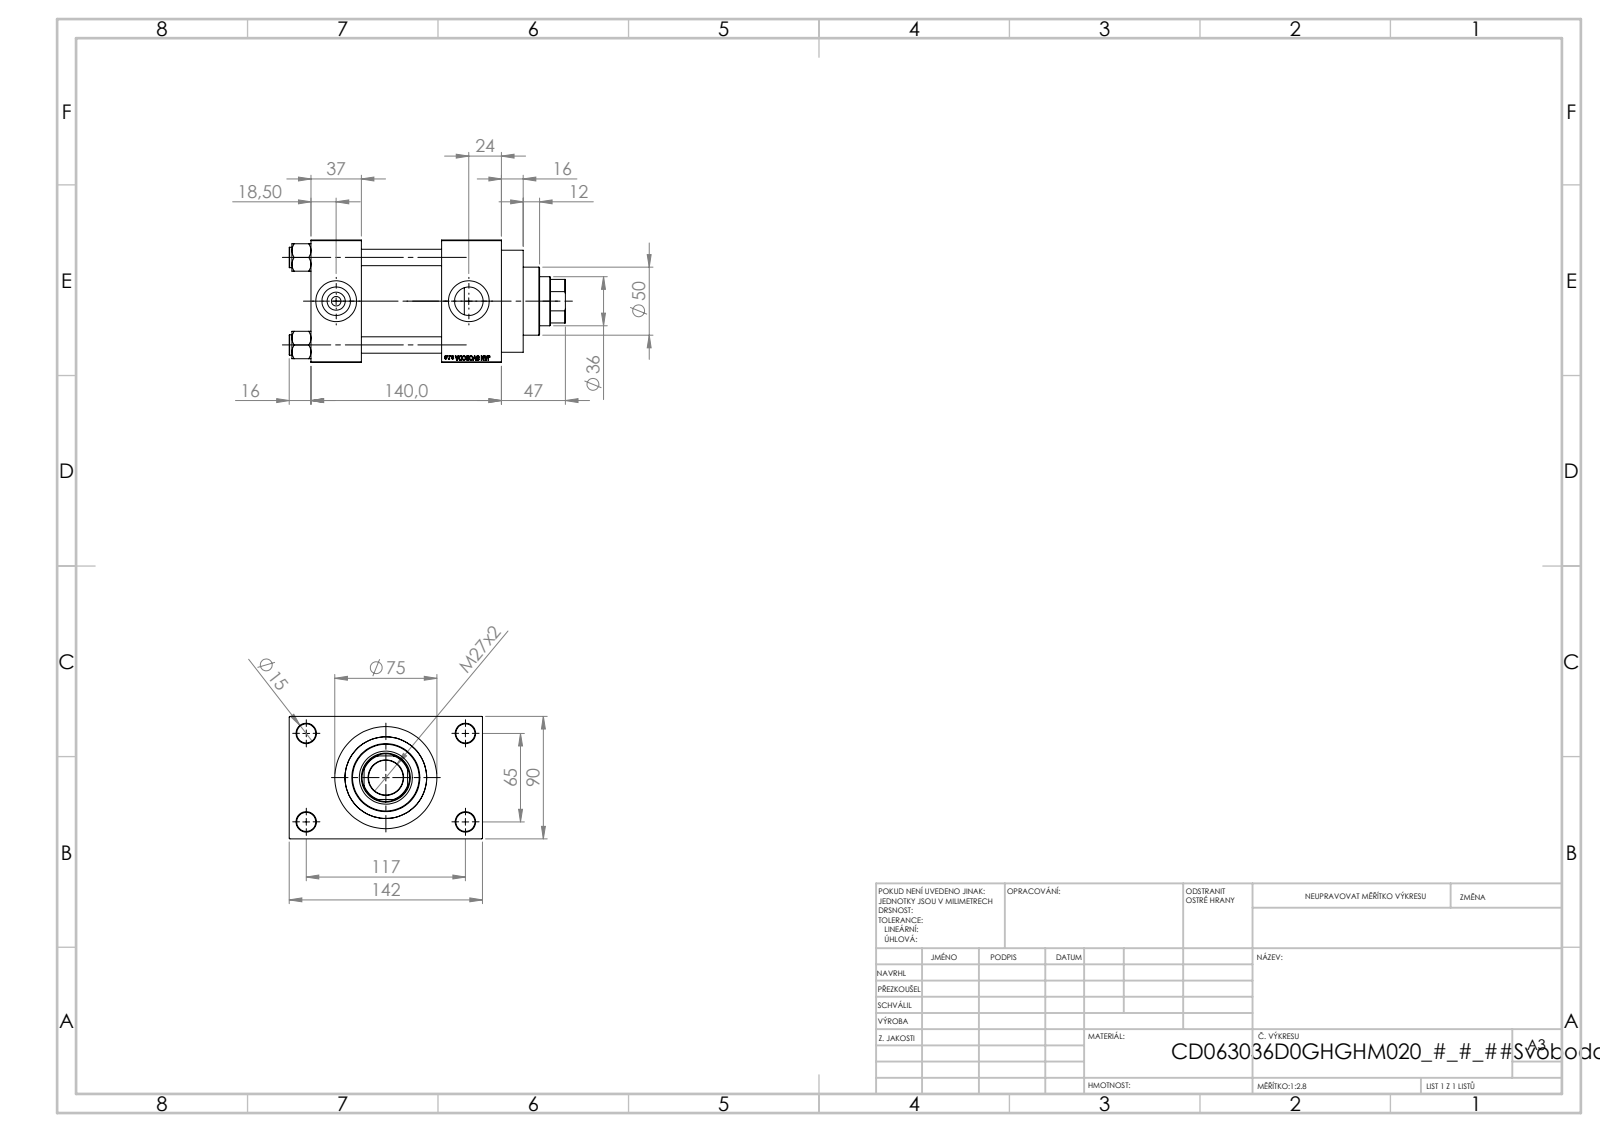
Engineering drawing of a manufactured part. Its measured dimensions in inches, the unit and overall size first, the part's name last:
Units: inches
Overall size (bounding box): 7.992 × 5.591 × 3.543
Round holes (diameter × count): ⌀0.472 ×4, ⌀0.551 ×4, ⌀0.276 ×2, ⌀0.825 ×2, ⌀1.181 ×2, ⌀1.004 ×1, ⌀1.417 ×1, ⌀1.535 ×1, ⌀1.969 ×1, ⌀2.362 ×1, ⌀2.48 ×1
Round bosses / shafts (diameter × count): ⌀0.591 ×4, ⌀2.953 ×1, ⌀2.717 ×1
Partial cylindrical surfaces — rounded edges, fillets, slot ends (radius × count): R0.689 ×1
Main face-to-face distances: 3.543, 2.323, 1.457, 3.78, 5.512, 4.055, 1.732, 1.024, 4.567, 5.591
Hole centre spacings: 1.037, 1.79, 2.531, 2.635, 2.748, 3.569, 4.383, 2.559
Volume: 67.86 in³ · Surface area: 319 in²
Bodies: 11 solids, 1103 faces (497 planar, 88 cylindrical, 518 other)
Part name (STEP PRODUCT): V215CD_D_Body; V215CD_NUT_M5_D; V215CD_D_TYCINKA; V215CD_VC_A (+1 more)
STEP written by: SolidWorks 2019 (CONFIG_CONTROL_DESIGN)
